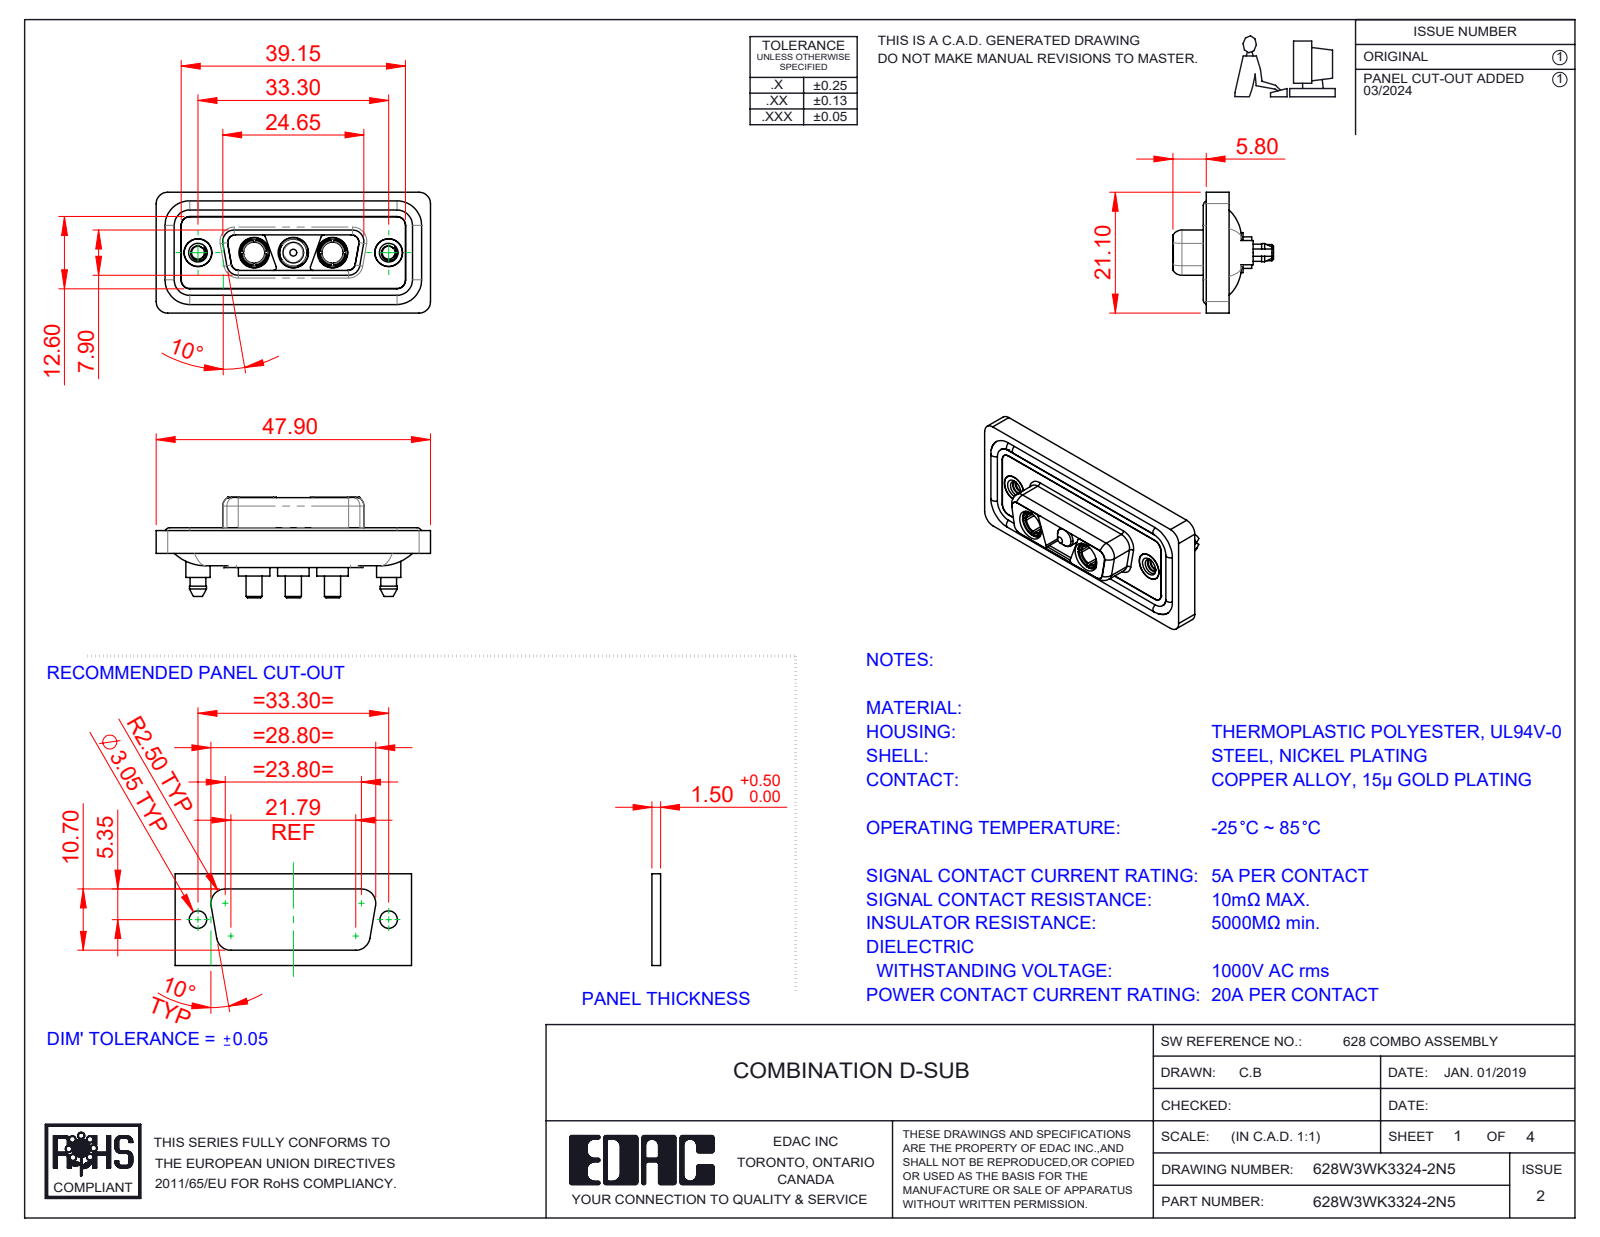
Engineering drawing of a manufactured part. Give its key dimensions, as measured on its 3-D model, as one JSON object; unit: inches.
{"part_name": "628Combo Threaded Boardlock_5; 628Combo Waterproof Housing_15 Contacts; 628W3WK3324-2N5; Power Pin_20A S (+4 more)", "step_written_by": "SolidWorks 2023 (CONFIG_CONTROL_DESIGN)", "units": "inches", "bodies": {"solids": 13, "faces": 633, "planar": 194, "cylindrical": 290, "other": 149}, "overall_size": [1.886, 0.831, 0.691], "volume_in3": 0.367, "surface_area_in2": 15.25, "round_holes": [[0.191, 5], [0.209, 3], [0.089, 2], [0.146, 2], [0.157, 2], [0.159, 2], [0.197, 2]], "round_bosses_or_shafts": [[0.063, 4], [0.217, 3], [0.205, 3], [0.187, 3], [0.148, 3], [0.11, 3], [0.213, 2], [0.195, 2]], "partial_cylinders_radius": [[0.059, 24], [0.079, 20], [0.053, 12], [0.063, 10], [0.02, 8], [0.01, 4], [0.024, 4], [0.026, 4]], "face_to_face_distances": [0.016, 0.063, 0.071, 0.02, 0.043, 0.114, 0.222, 0.278, 0.059, 0.211], "hole_center_spacings": [0.27, 0.386, 0.656, 0.925, 0.539, 1.311]}
